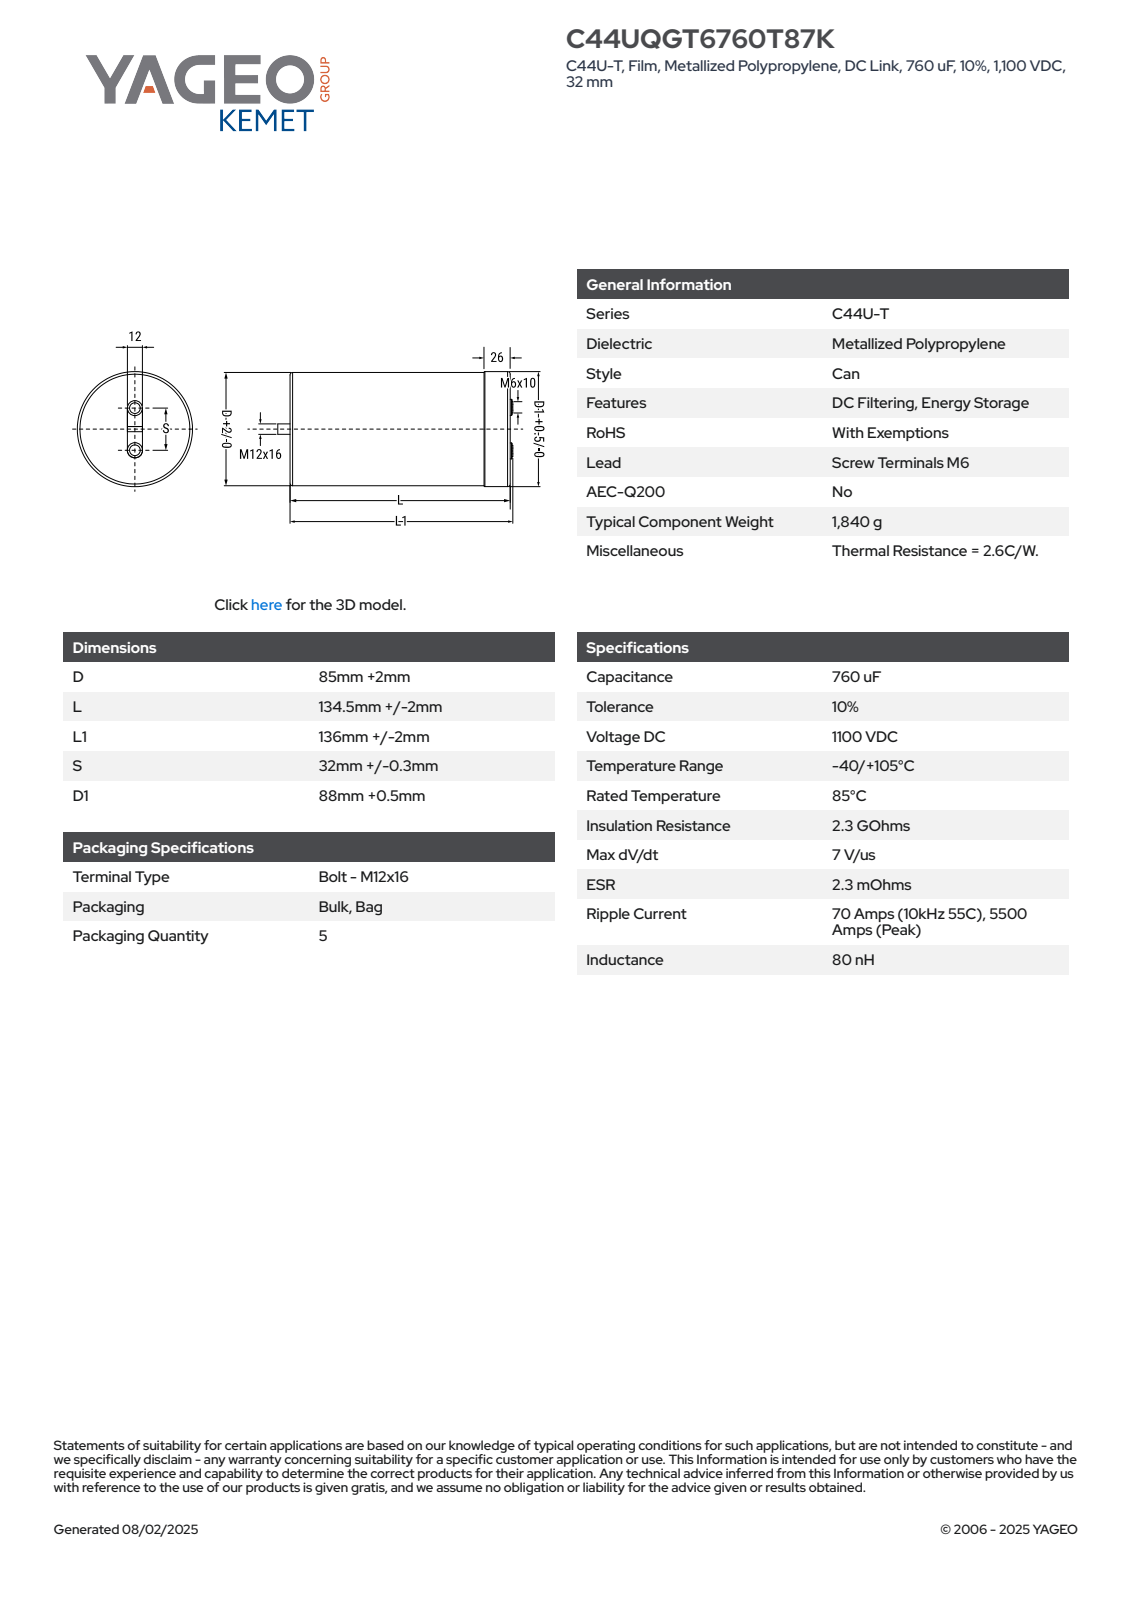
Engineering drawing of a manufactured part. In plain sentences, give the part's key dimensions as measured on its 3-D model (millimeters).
The part is named "CFP_C44UMR_85X134.5_D87L136.5S32L1138D188.5". Its 3-D file was written by "SolidWorks 2014 (AUTOMOTIVE_DESIGN)". It is 1 solid with 84 faces: 32 planar, 21 cylindrical and 31 other. Overall it measures 154 by 88.5 by 88.5 millimeters. Its volume is 818 385 cubic millimeters and its surface area 50 826 square millimeters. Round holes: 2 of diameter 6. Round bosses or shafts: 3 of diameter 12, 2 of diameter 10, 1 of diameter 88.5, 1 of diameter 87. Partial cylindrical surfaces (rounded edges, fillets, slot ends): 1 of radius 43.51. The main face-to-face distances are 136.5, 110.5, 26, 16, 126.5, 152.5, 154, 138, 27.5, 1.5. The hole center spacings are 32.
